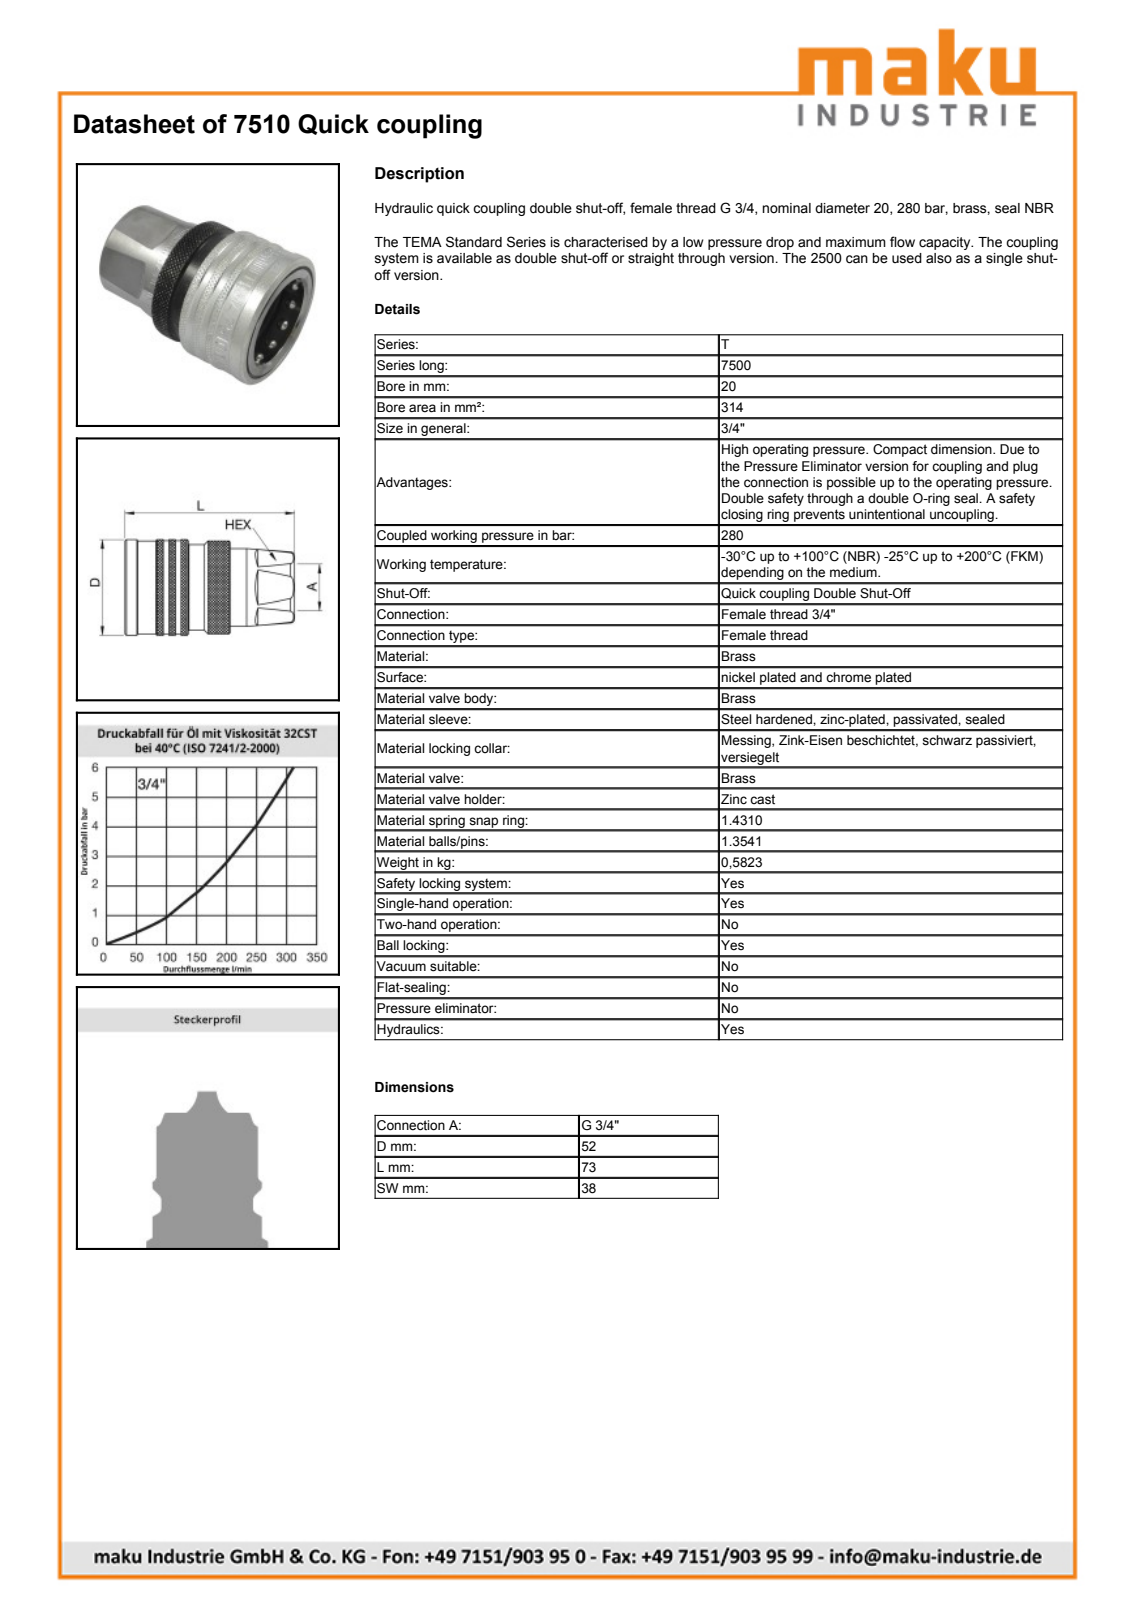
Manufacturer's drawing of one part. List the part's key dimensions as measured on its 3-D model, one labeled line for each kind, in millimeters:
Part name (STEP PRODUCT): 7510
STEP written by: SolidWorks 2009 (AUTOMOTIVE_DESIGN)
Units: millimetres
Bodies: 1 solid, 127 faces (31 planar, 42 cylindrical, 54 other)
Overall size (bounding box): 73 × 52 × 52
Volume: 88 168 mm³ · Surface area: 21 703 mm²
Round holes (diameter × count): ⌀19 ×1, ⌀24.1 ×1, ⌀32.8 ×1, ⌀32.9 ×1, ⌀34.8 ×1, ⌀35.6 ×1, ⌀37.9 ×1, ⌀44.7 ×1, ⌀45.7 ×1
Round bosses / shafts (diameter × count): ⌀52 ×1, ⌀51.2 ×1, ⌀51 ×1, ⌀49 ×1, ⌀46 ×1, ⌀45.6 ×1, ⌀43.5 ×1, ⌀41.5 ×1
Main face-to-face distances: 38, 44, 18, 26, 73, 55, 29, 44.75, 26.75, 0.75
